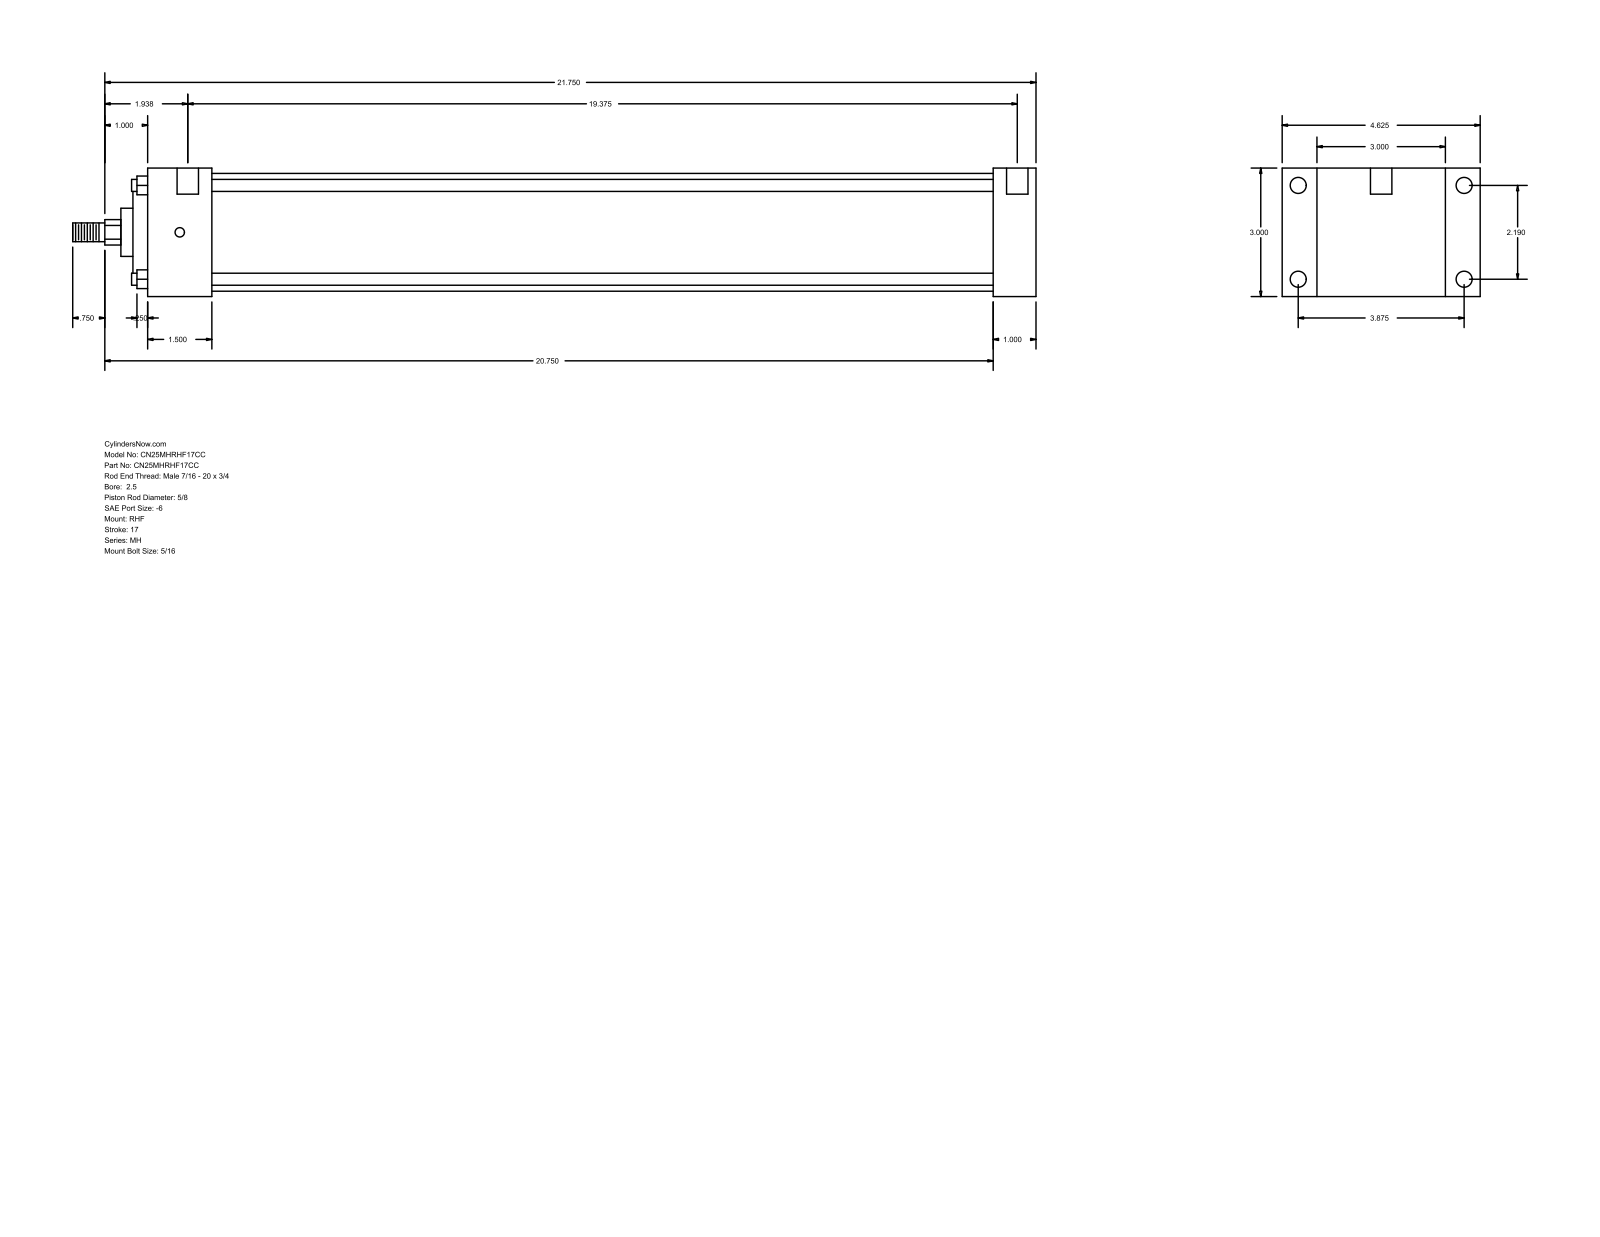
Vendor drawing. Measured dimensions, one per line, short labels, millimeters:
name: MH_RHF__0250_0.625
written by: GSSL Pune (CONFIG_CONTROL_DESIGN)
unit: mm
bodies: 0 solids, 90 faces (61 planar, 29 cylindrical, 0 other)
size: 571.5 × 117.47 × 76.2
holes: 4× ⌀5.56, 4× ⌀9.53, 2× ⌀12.7
bosses: 4× ⌀7.14, 1× ⌀69.85, 1× ⌀55.55, 1× ⌀28.57, 1× ⌀15.88, 1× ⌀11.11
rounds: 1× R7.54
face distances: 76.2, 25.4, 20.64, 96.84, 527.05, 501.65, 38.1, 117.48, 463.55, 488.95
hole spacings: 55.62, 98.42, 113.05, 500.06, 3.17, 4.76, 492.13, 495.3
